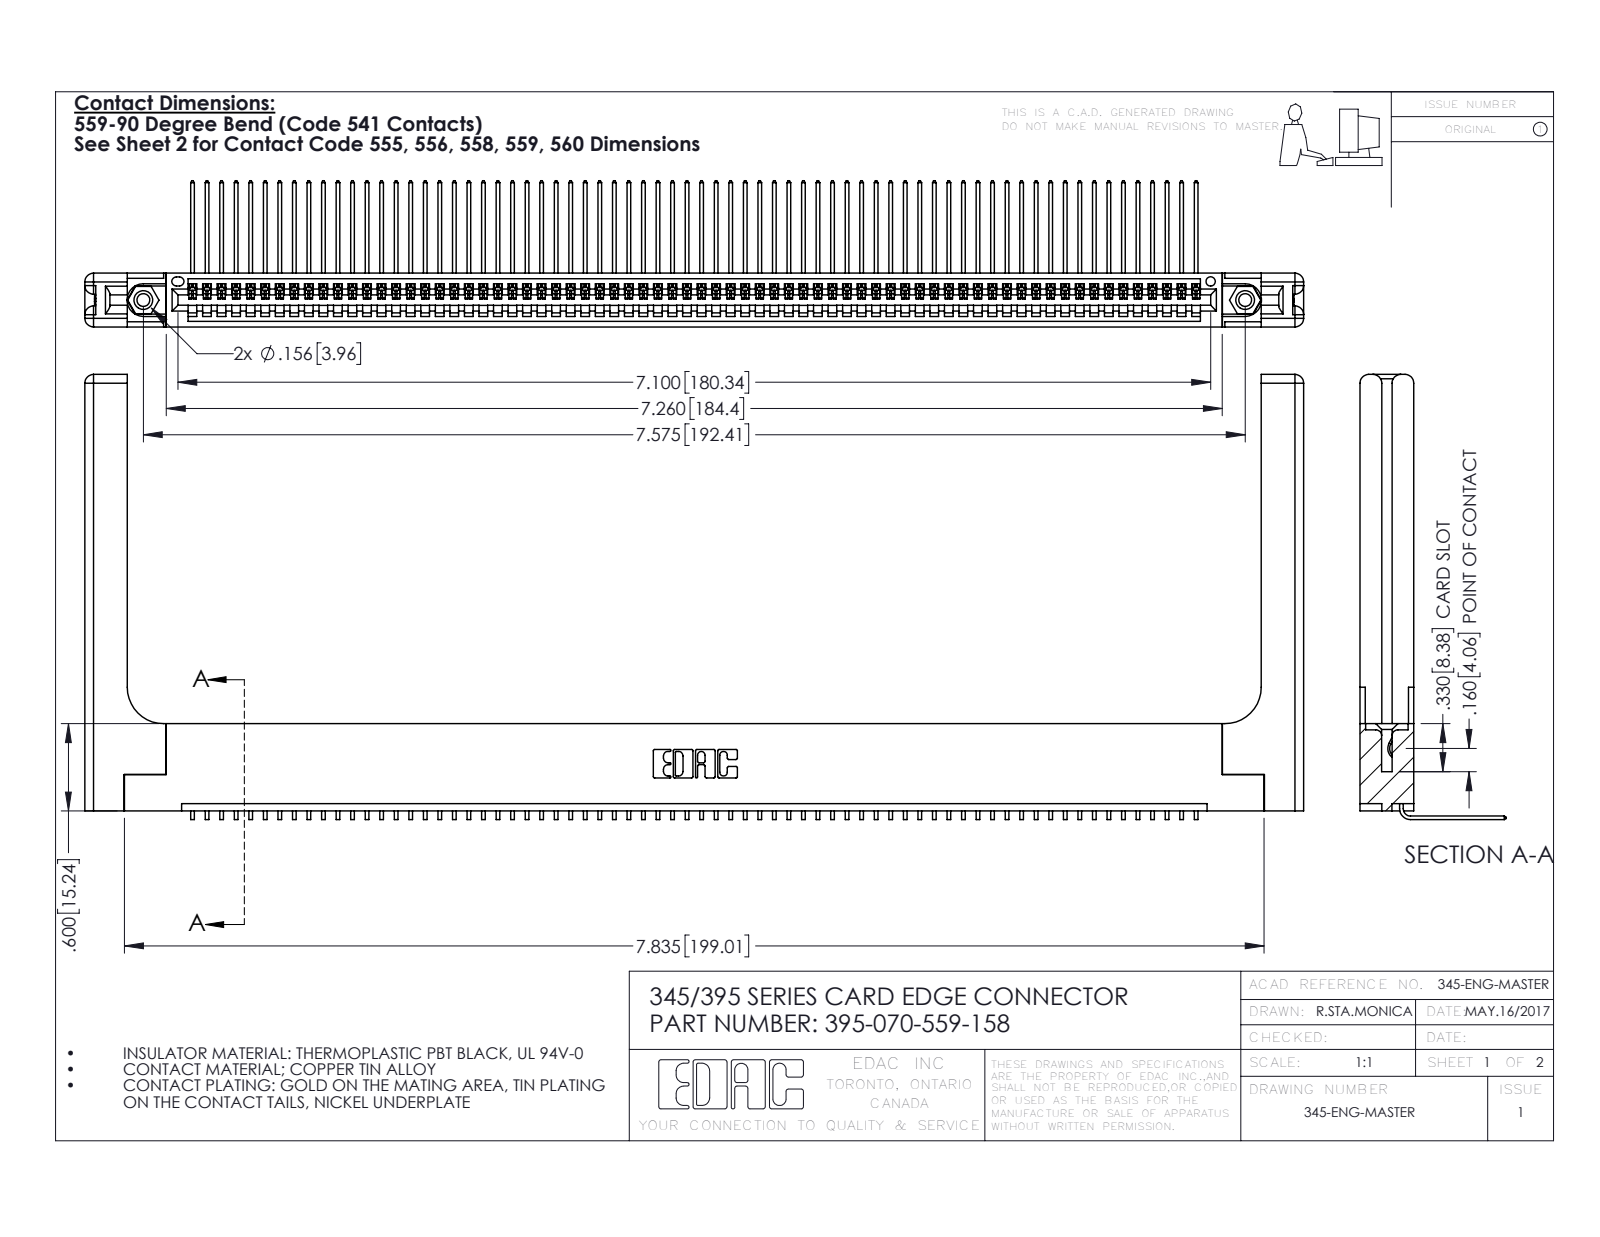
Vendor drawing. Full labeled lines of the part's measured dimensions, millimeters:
Part name (STEP PRODUCT): 395-070-559-158; 345 Part_Flush Mounting Lugs - 0.156 Dia-TH; 345-220-058_345-220-058; 345-250-001_345-250-001-102 (+1 more)
STEP written by: SolidWorks 2016 (CONFIG_CONTROL_DESIGN)
Units: millimetres
Bodies: 75 solids, 4582 faces (3168 planar, 1354 cylindrical, 60 other)
Overall size (bounding box): 212.8 × 77.7 × 25.5
Volume: 29 190 mm³ · Surface area: 34 540 mm²
Round holes (diameter × count): ⌀2.3 ×2, ⌀3.2 ×2, ⌀4 ×2, ⌀1.6 ×1
Round bosses / shafts (diameter × count): ⌀3.9 ×2
Partial cylindrical surfaces — rounded edges, fillets, slot ends (radius × count): R0.2 ×140, R0.3 ×22, R1.5 ×16, R0.2 ×6, R0.8 ×6, R0.7 ×3, R0.8 ×2, R0.8 ×2
Main face-to-face distances: 1.8, 9.4, 7.6, 5.1, 2.5, 6.9, 0.6, 5.7, 3.8, 3.8
Hole centre spacings: 6.9, 186.4, 192.4
